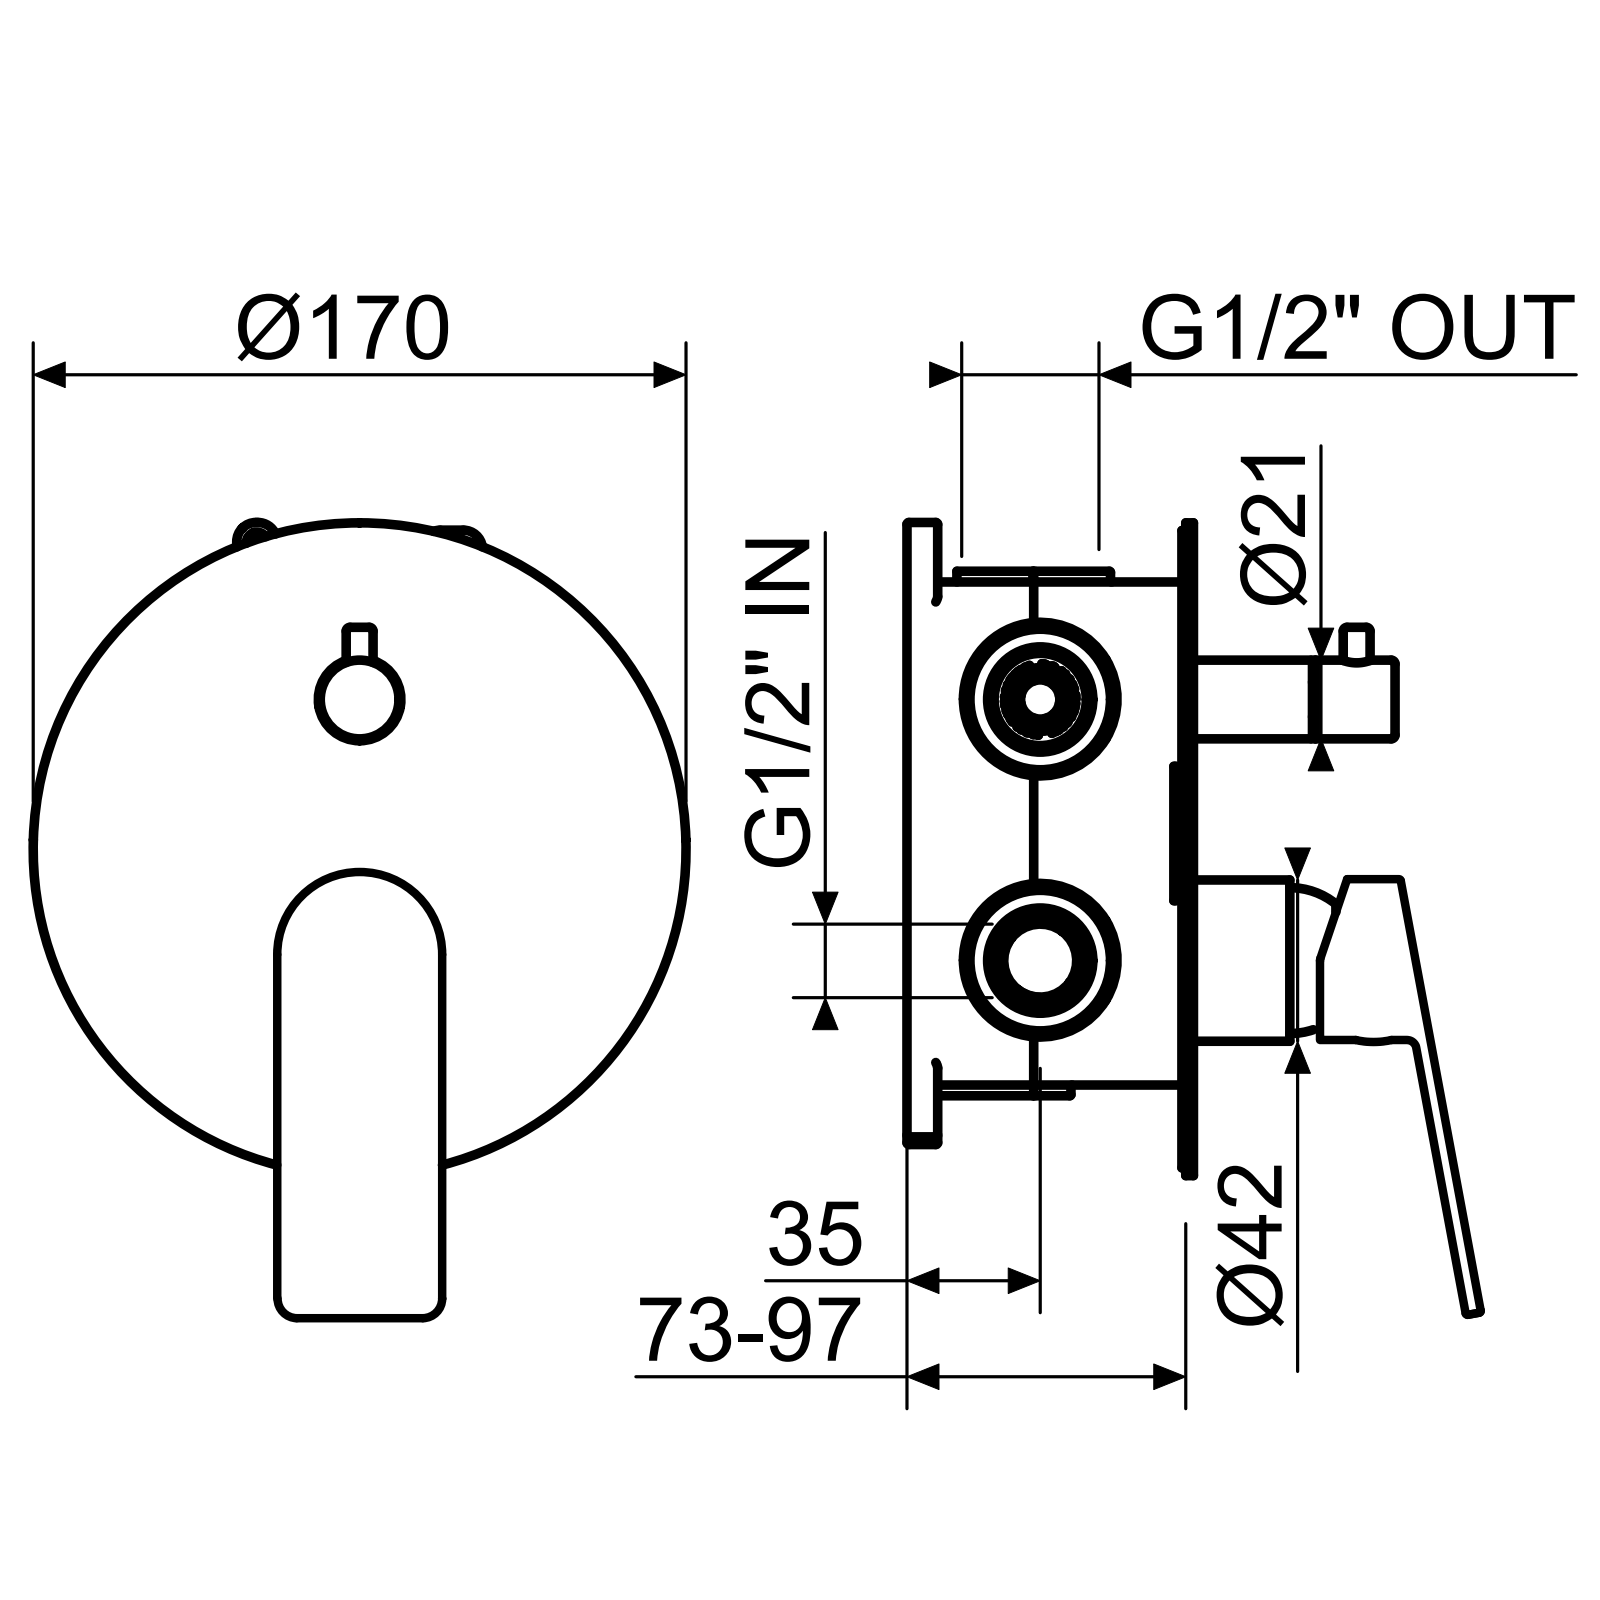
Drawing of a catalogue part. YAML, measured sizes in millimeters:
part_name: "SINMAC0008; SCCMAC0005; ATAO005C001; SPLMAC0001 (+8 more)"
step_written_by: "CREO PARAMETRIC BY PTC INC, 2020281 (CONFIG_CONTROL_DESIGN)"
units: millimeters
bodies: {solids: 10, faces: 366, planar: 65, cylindrical: 116, other: 185}
overall_size: [205.58, 170, 81.09]
volume: 76147
surface_area: 87514
round_holes:
  - {diameter: 4.2, count: 2}
  - {diameter: 8, count: 2}
  - {diameter: 5, count: 1}
  - {diameter: 5.2, count: 1}
  - {diameter: 6.5, count: 1}
  - {diameter: 7.5, count: 1}
  - {diameter: 12, count: 1}
  - {diameter: 14, count: 1}
  - {diameter: 18, count: 1}
  - {diameter: 21.5, count: 1}
  - {diameter: 22, count: 1}
  - {diameter: 25, count: 1}
round_bosses_or_shafts:
  - {diameter: 170, count: 1}
  - {diameter: 49, count: 1}
  - {diameter: 42, count: 1}
  - {diameter: 34, count: 1}
  - {diameter: 27.5, count: 1}
  - {diameter: 20.5, count: 1}
  - {diameter: 7, count: 1}
  - {diameter: 5, count: 1}
partial_cylinders:
  - {radius: 0.5, count: 23}
  - {radius: 1.6, count: 6}
  - {radius: 3, count: 4}
  - {radius: 0.3, count: 2}
  - {radius: 1, count: 2}
  - {radius: 1.5, count: 2}
  - {radius: 177.03, count: 2}
  - {radius: 2.55, count: 1}
face_to_face_distances: [2, 4, 6, 30.1, 1, 31.1, 5, 29.1, 47.5, 53.5]
hole_center_spacings: [5.1, 68]
